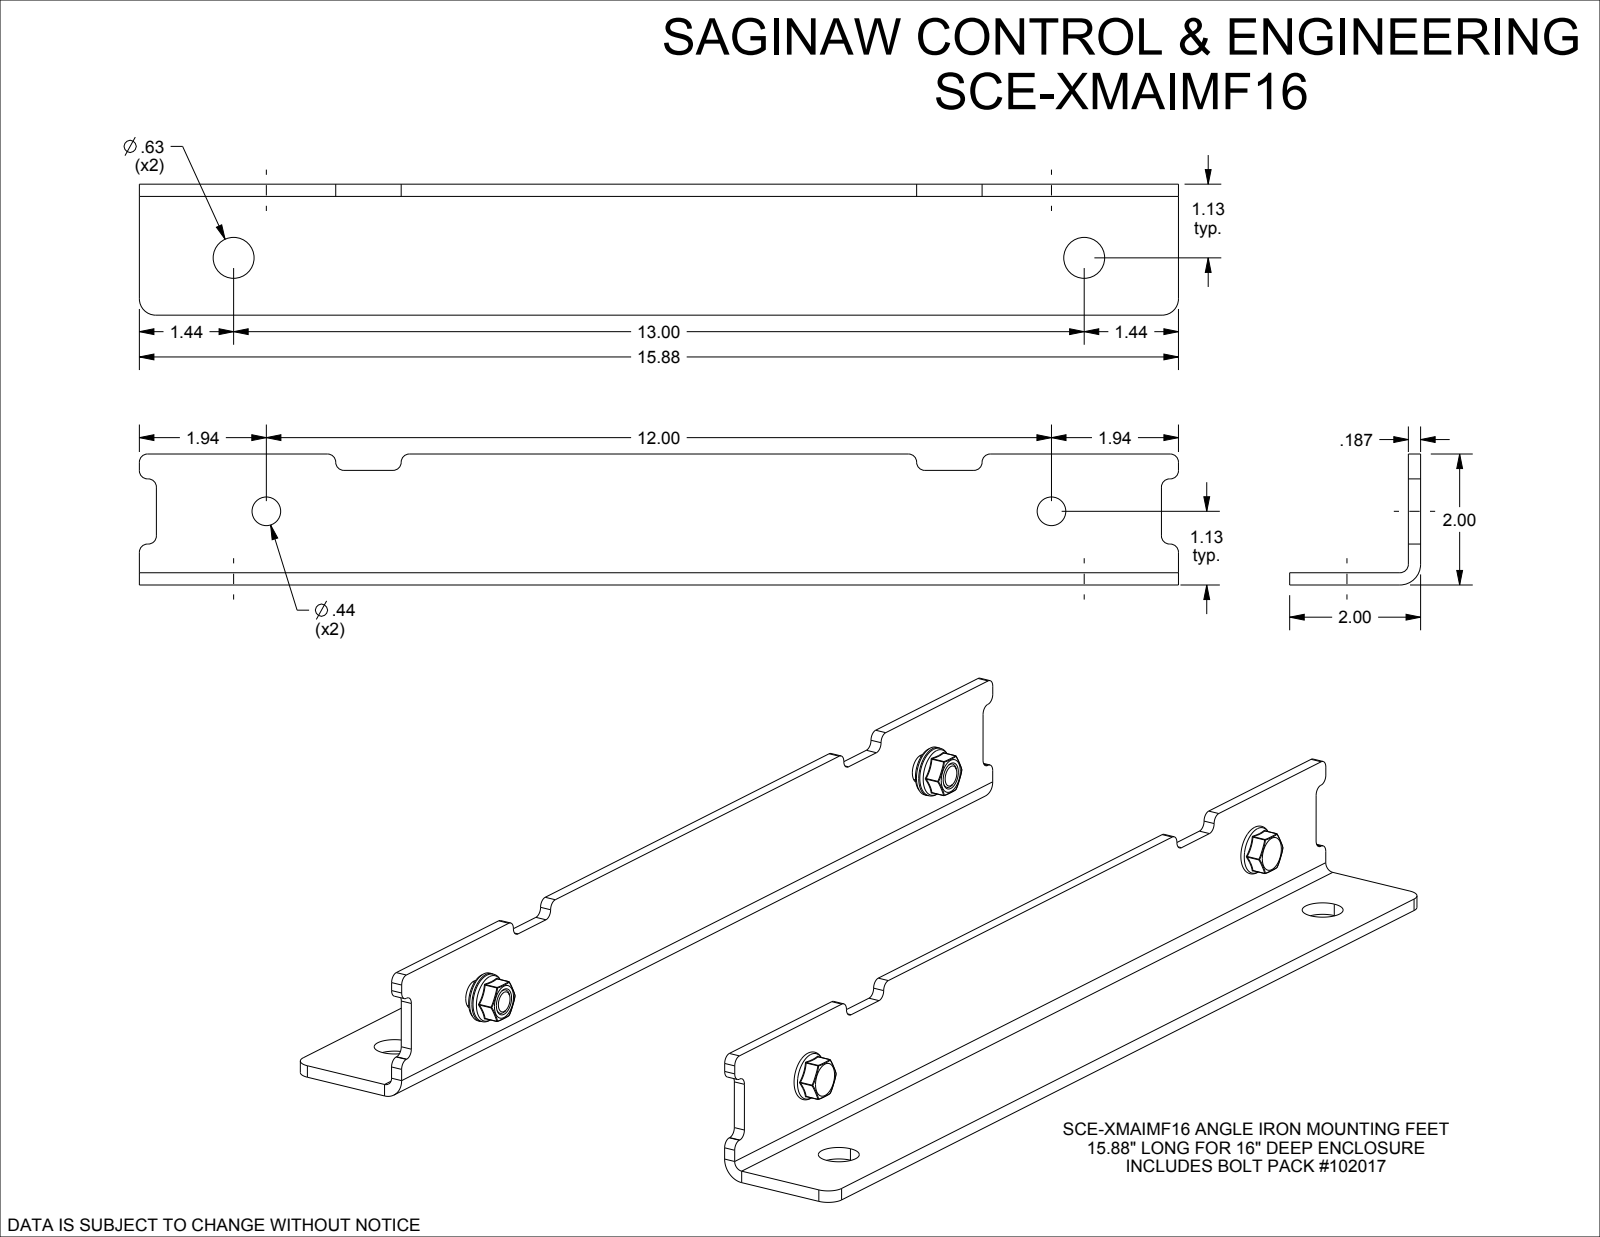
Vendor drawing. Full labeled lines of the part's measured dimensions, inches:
Part name (STEP PRODUCT): SCE-XMAIMF16
STEP written by: SolidWorks 2019 (CONFIG_CONTROL_DESIGN)
Units: inches
Bodies: 14 solids, 476 faces (124 planar, 124 cylindrical, 228 other)
Overall size (bounding box): 15.875 × 10 × 2
Volume: 22.43 in³ · Surface area: 264.7 in²
Round holes (diameter × count): ⌀0.367 ×2, ⌀0.4 ×2, ⌀0.43 ×2, ⌀0.437 ×2, ⌀0.625 ×2, ⌀0.625 ×2
Round bosses / shafts (diameter × count): ⌀0.75 ×2, ⌀0.7 ×2, ⌀0.373 ×2
Partial cylindrical surfaces — rounded edges, fillets, slot ends (radius × count): R0.125 ×23, R0.01 ×18, R0.25 ×4, R0.13 ×2, R0.317 ×2
Main face-to-face distances: 0.187, 6.187, 6.374, 6, 1.813, 2, 8, 8.187, 10.001, 2.223
Hole centre spacings: 8.25, 12.995, 15.393, 11.995, 12
